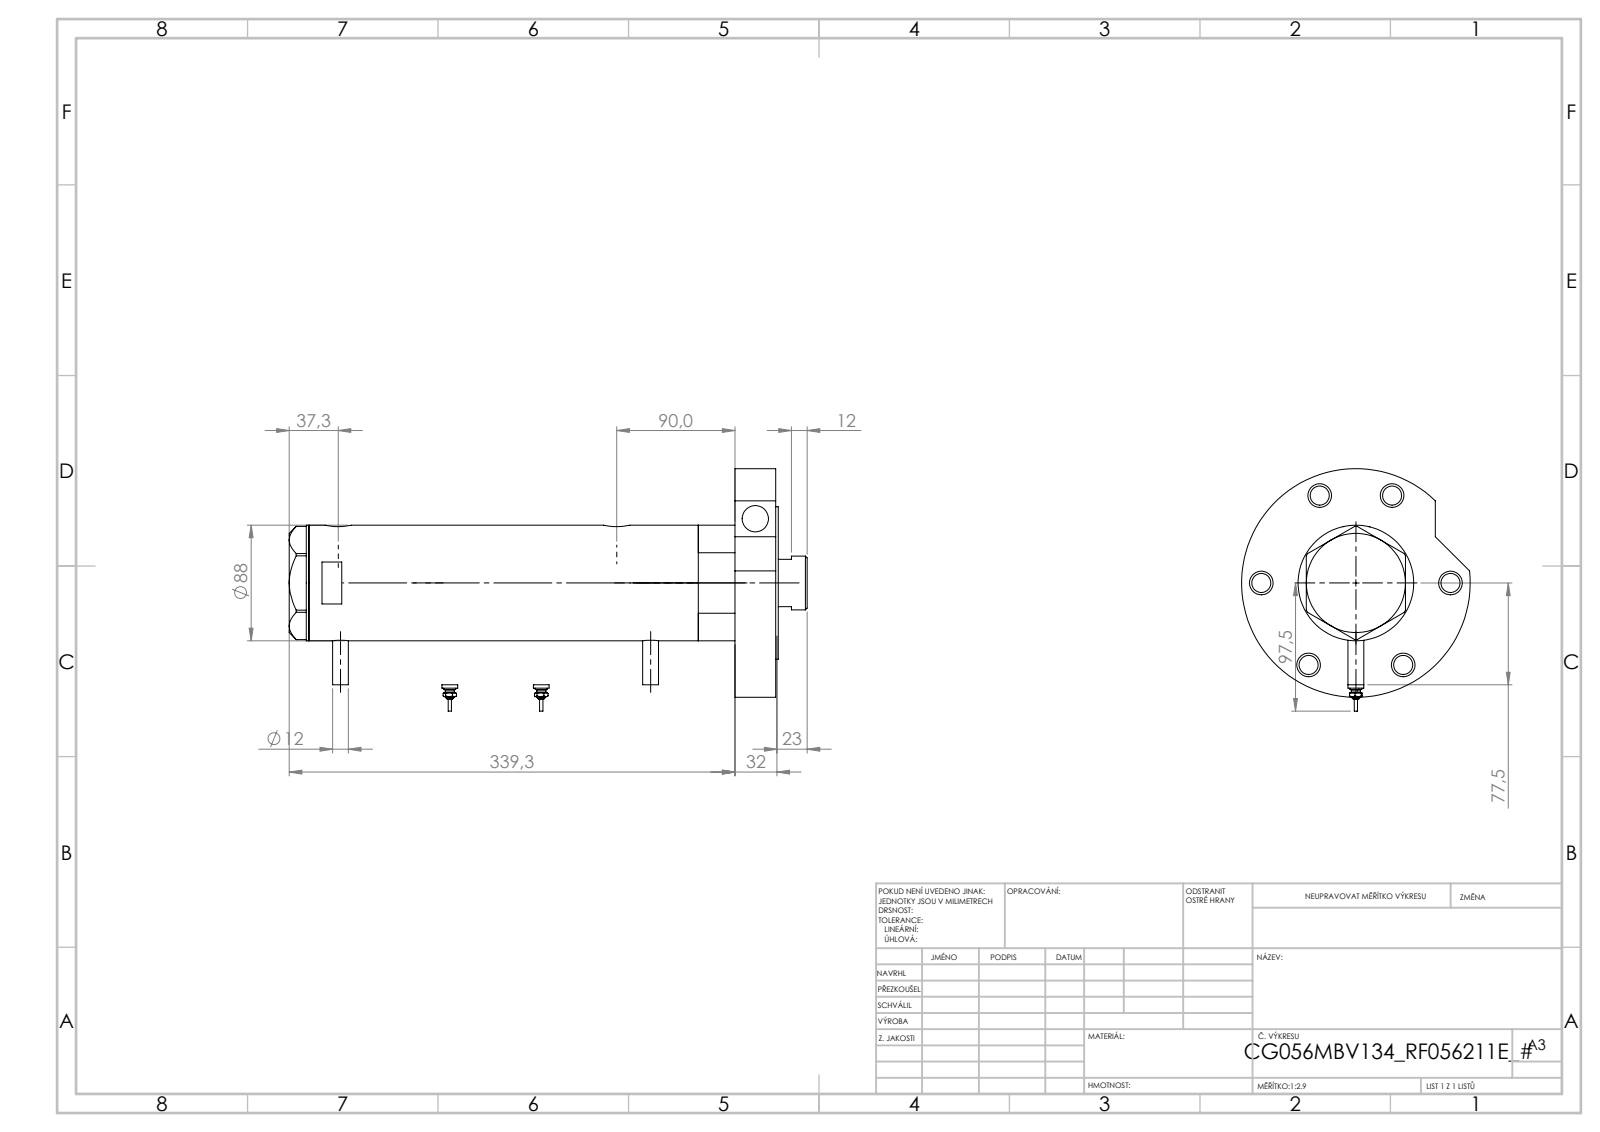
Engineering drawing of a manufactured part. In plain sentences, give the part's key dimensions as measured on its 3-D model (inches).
The part is named "V270CG_RF211E; V270CG_VC; V270CG_BACK; V270CG_MIDDLE (+2 more)". Its 3-D file was written by "SolidWorks 2019 (CONFIG_CONTROL_DESIGN)". It is 7 solids with 257 faces: 91 planar, 102 cylindrical and 64 other. Overall it measures 15.524 by 7.264 by 6.85 inches. Its volume is 157.3 cubic inches and its surface area 560.2 square inches. Round holes: 7 of diameter 0.571, 6 of diameter 0.709, 3 of diameter 0.787, 2 of diameter 0.492, 2 of diameter 0.518, 1 of diameter 1.654, 1 of diameter 1.713, 1 of diameter 2.205, 1 of diameter 2.362, 1 of diameter 2.953, 1 of diameter 3.15. Round bosses or shafts: 4 of diameter 0.472, 2 of diameter 0.354, 2 of diameter 0.276, 2 of diameter 0.177, 2 of diameter 0.098, 1 of diameter 6.85, 1 of diameter 4.567, 1 of diameter 3.465. The main face-to-face distances are 1.22, 0.079, 14.067, 12.768, 13.988, 1.299, 9.228, 3.539, 4.76, 4.839. The hole center spacings are 2.835, 3.15, 4.714, 4.91, 5.085, 5.657, 0.067, 1.016.
